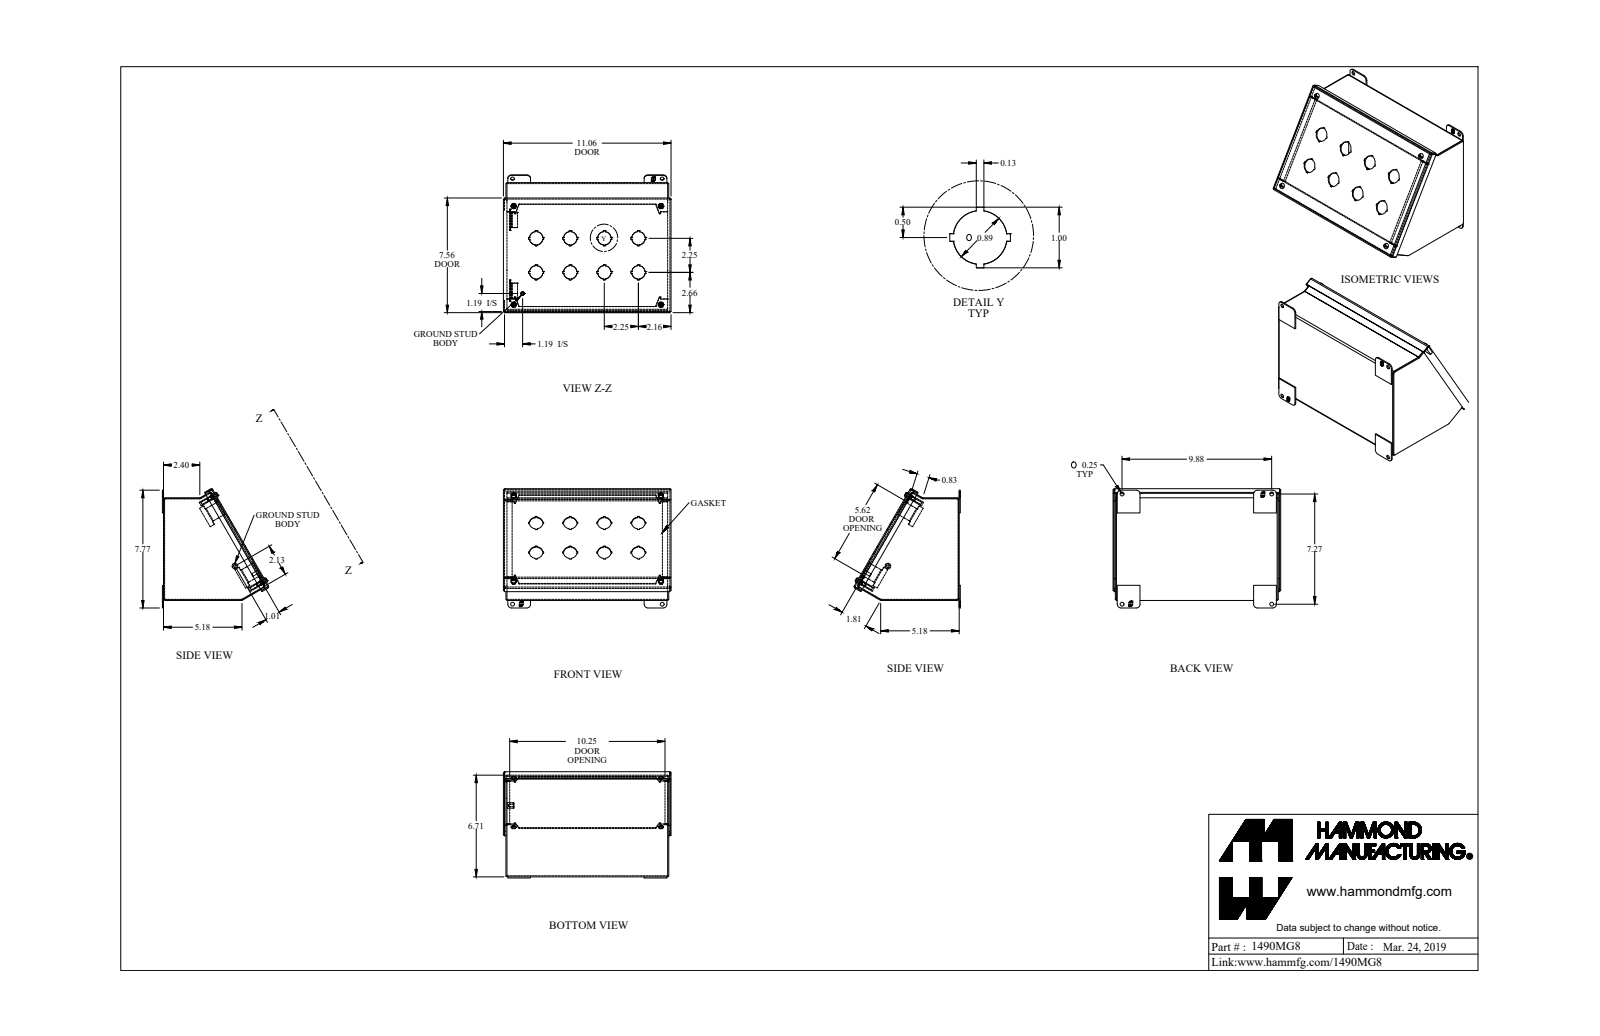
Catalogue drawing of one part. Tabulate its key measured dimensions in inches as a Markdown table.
| quantity | value |
| --- | --- |
| part name | 1490MG8_Default |
| STEP written by | SolidWorks 2019 (CONFIG_CONTROL_DESIGN) |
| units | inches |
| bodies | 26 solids, 822 faces (579 planar, 205 cylindrical, 38 other) |
| overall size | 11.062 × 7.911 × 7.088 |
| volume | 26.26 in³ |
| surface area | 750.2 in² |
| round holes (diameter × count) | 0.25 × 8, 0.875 × 5, 0.159 × 4, 0.875 × 3, 0.12 × 1, 0.136 × 1, 0.156 × 1 |
| round bosses / shafts (diameter × count) | 0.39 × 4, 0.275 × 4, 0.19 × 4, 0.148 × 4, 0.375 × 1, 0.29 × 1 |
| partial cylindrical surfaces (radius × count) | 0.108 × 18, 0.036 × 12, 0.029 × 8, 0.086 × 8, 0.25 × 8, 0.125 × 4, 0.16 × 4, 0.171 × 4 |
| main face-to-face distances | 0.072, 10.678, 6.697, 10.606, 10.75, 6.769, 6.625, 0.156, 7.334, 0.228 |
| hole center spacings | 2.25, 3.182, 6.5, 4.5, 5.031, 9.717, 11.691, 2.59 |
